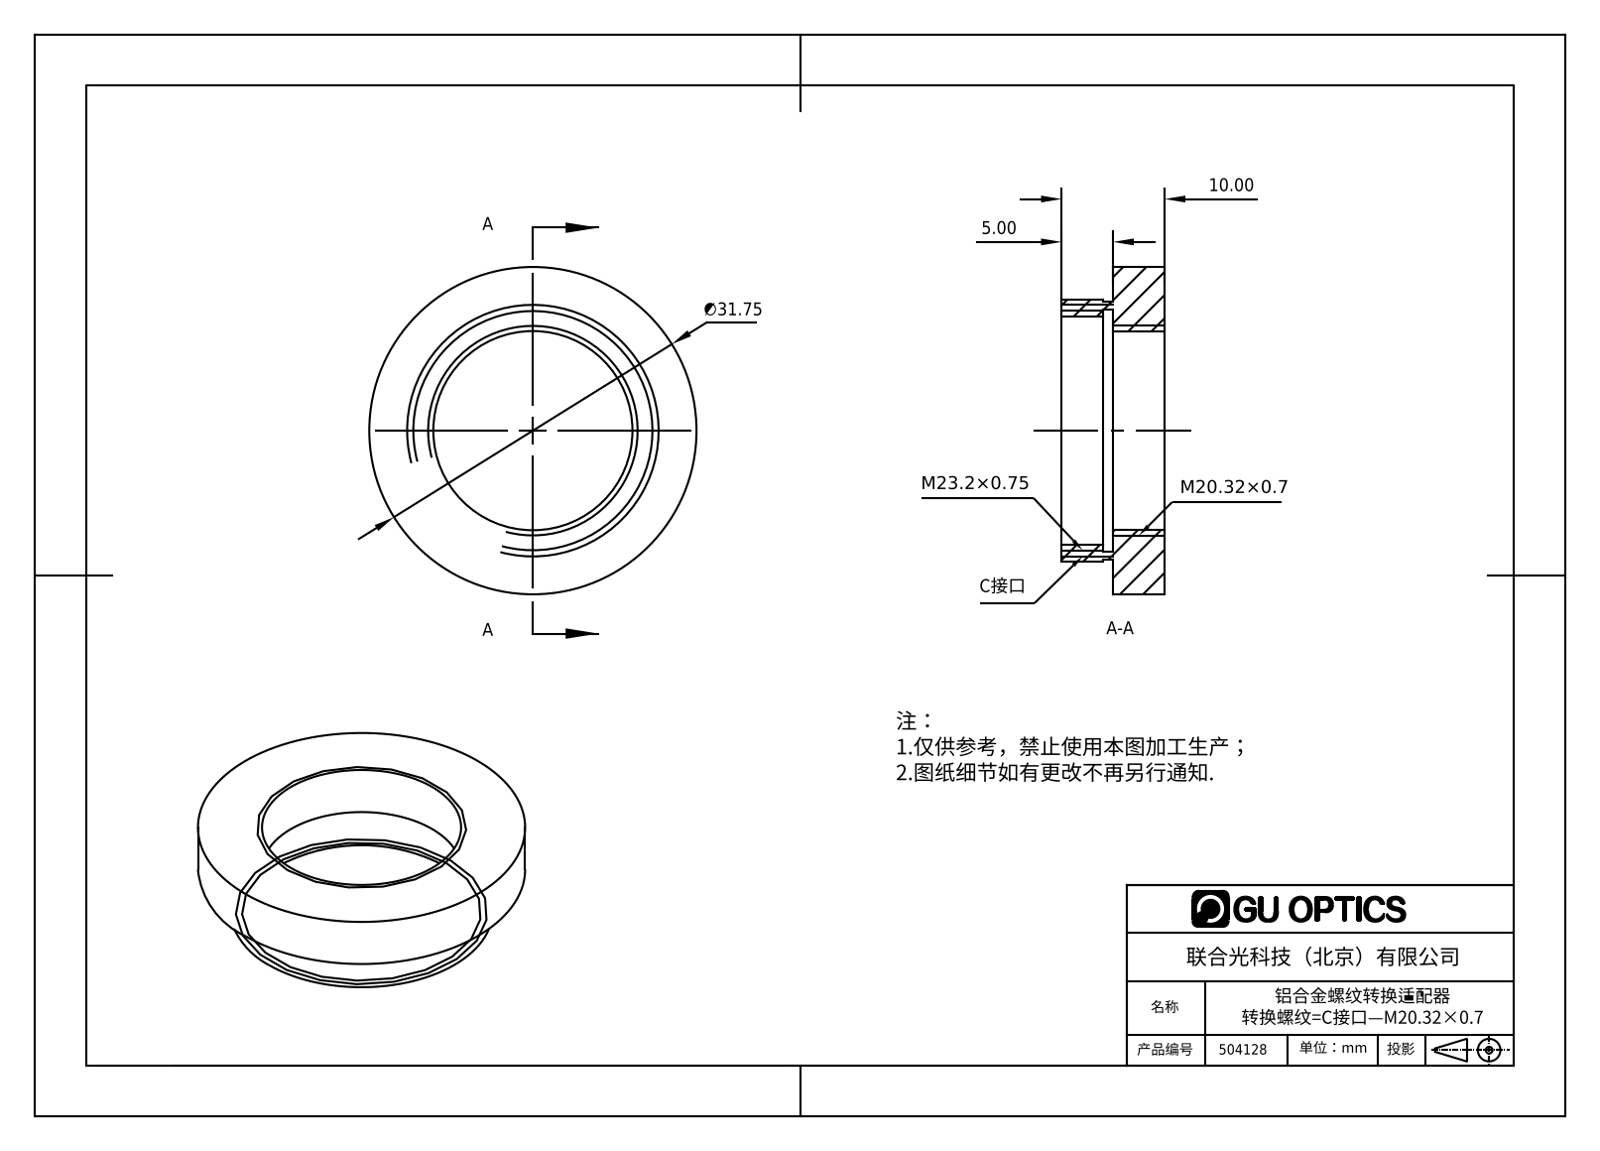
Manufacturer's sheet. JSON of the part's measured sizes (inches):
{"part_name": "504128", "step_written_by": "SolidWorks 2016 (AUTOMOTIVE_DESIGN)", "units": "inches", "bodies": {"solids": 1, "faces": 18, "planar": 6, "cylindrical": 12, "other": 0}, "overall_size": [1.25, 1.25, 0.394], "volume_in3": 0.185, "surface_area_in2": 4.123, "round_holes": [[0.761, 1], [0.874, 1], [0.921, 1]], "round_bosses_or_shafts": [[1.25, 1], [1, 1], [0.988, 1]], "face_to_face_distances": [0.197, 0.394, 0.157, 0.039, 0.236]}
